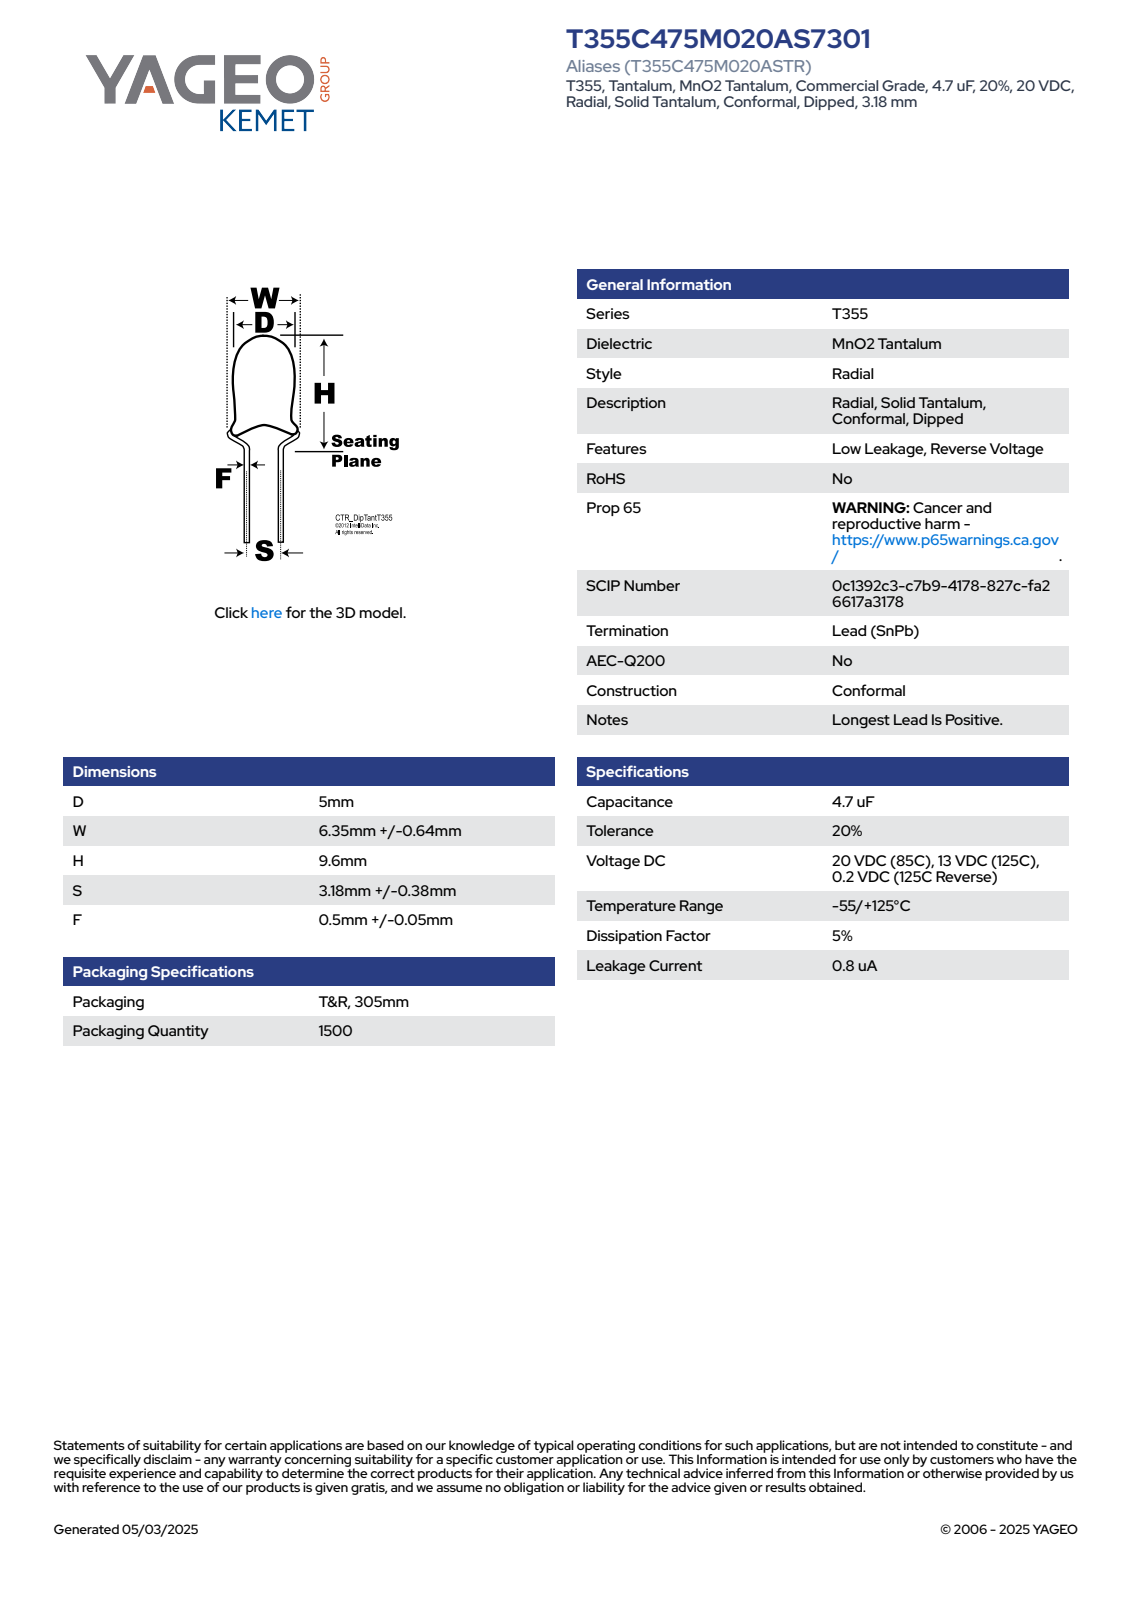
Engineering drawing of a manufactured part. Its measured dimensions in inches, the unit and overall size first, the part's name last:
Units: inches
Overall size (bounding box): 0.597 × 0.275 × 0.197
Round bosses / shafts (diameter × count): ⌀0.197 ×1
Partial cylindrical surfaces — rounded edges, fillets, slot ends (radius × count): R0.098 ×1
Main face-to-face distances: 0.264, 0.333, 0.597, 0.48, 0.147, 0.117, 0.456, 0.123, 0.024, 0.141
Volume: 0.007 in³ · Surface area: 0.242 in²
Bodies: 1 solid, 100 faces (30 planar, 6 cylindrical, 64 other)
Part name (STEP PRODUCT): CTR_T355_D5W6.99H9.6S3.18LL5.56F0.55
STEP written by: SolidWorks 2021 (AUTOMOTIVE_DESIGN)
